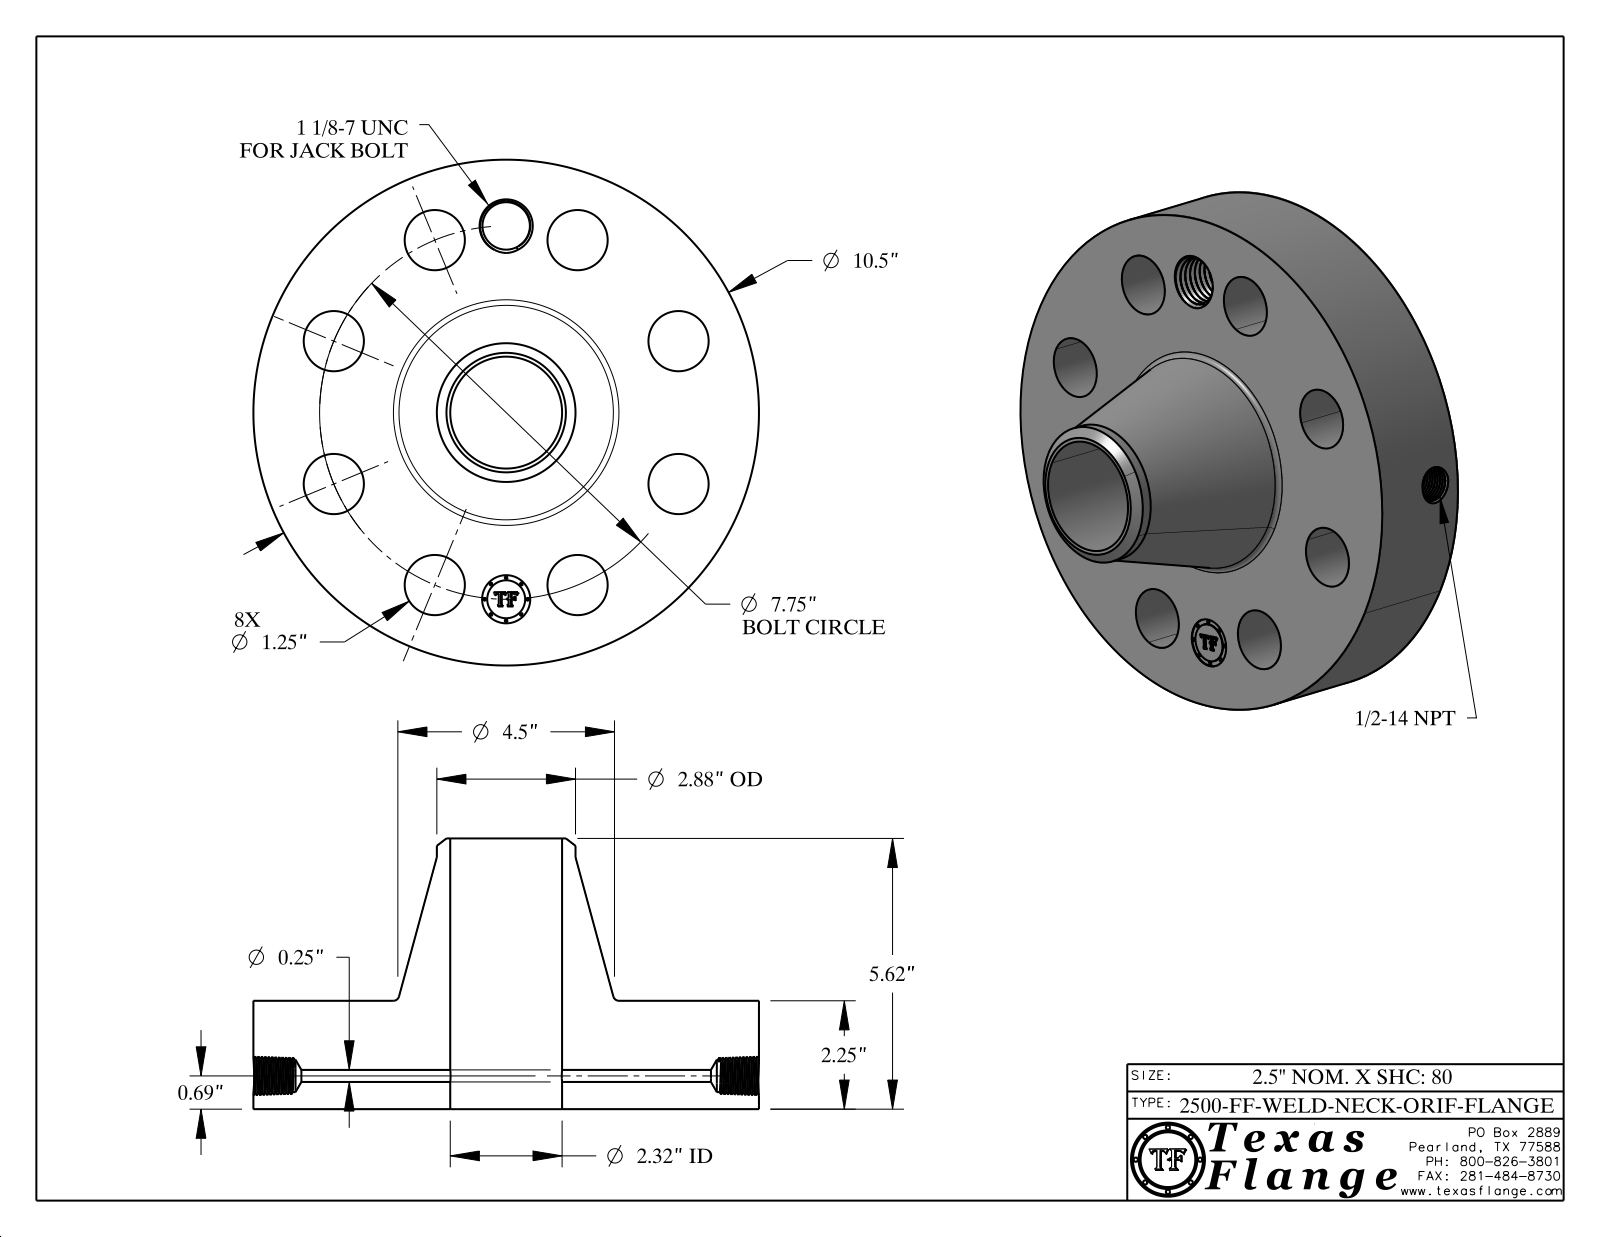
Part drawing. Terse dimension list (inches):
name: 2500-FF-WELD-NECK
written by: CATIA V5 STEP AP214 (AUTOMOTIVE_DESIGN)
unit: in
bodies: 1 solid, 772 faces (368 planar, 93 cylindrical, 311 other)
size: 10.5 × 10.5 × 5.62
volume: 180.7 in³; area: 380.2 in²
holes: 8× ⌀1.25, 1× ⌀0.25, 1× ⌀0.672, 1× ⌀0.984, 1× ⌀1, 1× ⌀2.323
bosses: 8× ⌀0.061, 1× ⌀10.5, 1× ⌀2.88, 1× ⌀0.788
face distances: 2.25, 5.62, 3.37, 0.015, 2.235, 3.385, 0.298, 0.292, 0.054, 0.248
hole spacings: 3.875, 5.48, 1.512, 2.965, 2.966, 4.306, 6.444, 7.16
